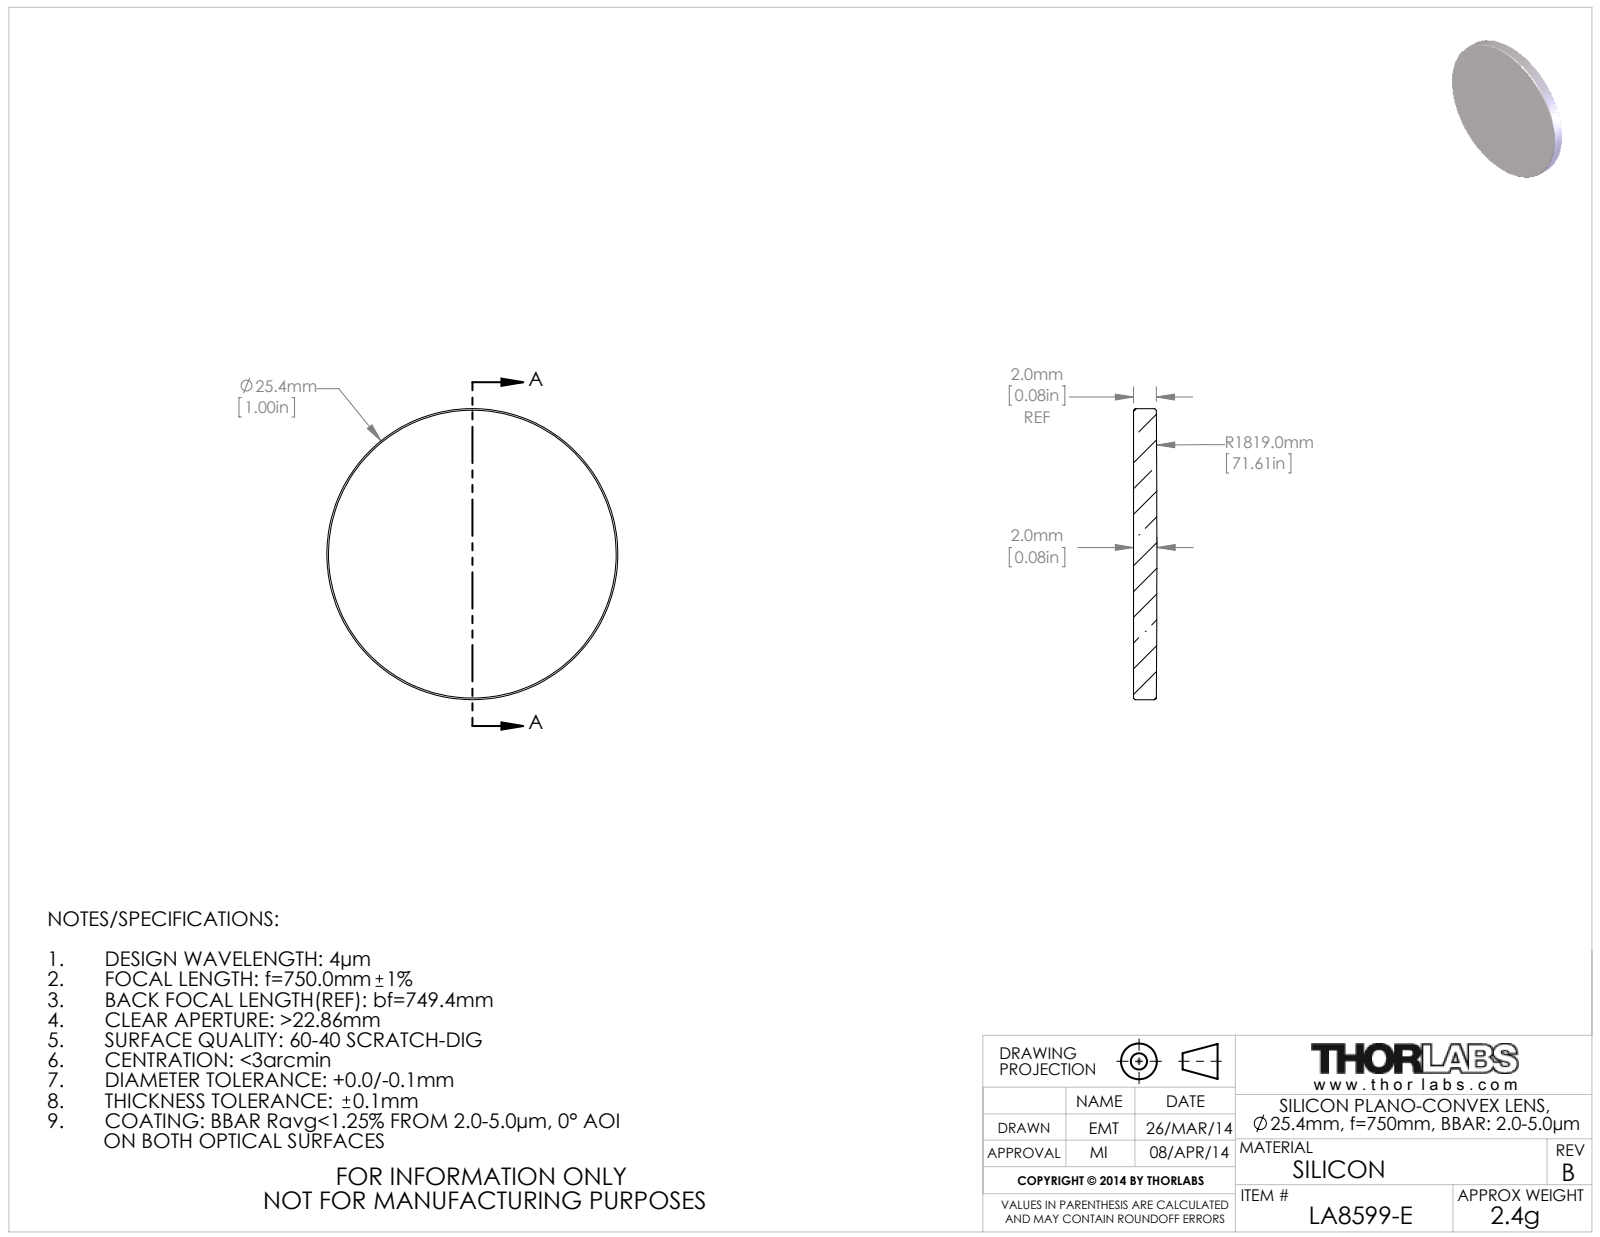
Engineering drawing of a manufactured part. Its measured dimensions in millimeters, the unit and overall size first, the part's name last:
Units: millimetres
Overall size (bounding box): 25.4 × 25.4 × 2.04
Round bosses / shafts (diameter × count): ⌀25.4 ×1
Volume: 1 021 mm³ · Surface area: 1 159 mm²
Bodies: 1 solid, 9 faces (1 planar, 2 cylindrical, 6 other)
Part name (STEP PRODUCT): 20123-E0W
STEP written by: SolidWorks 2014 (CONFIG_CONTROL_DESIGN)
